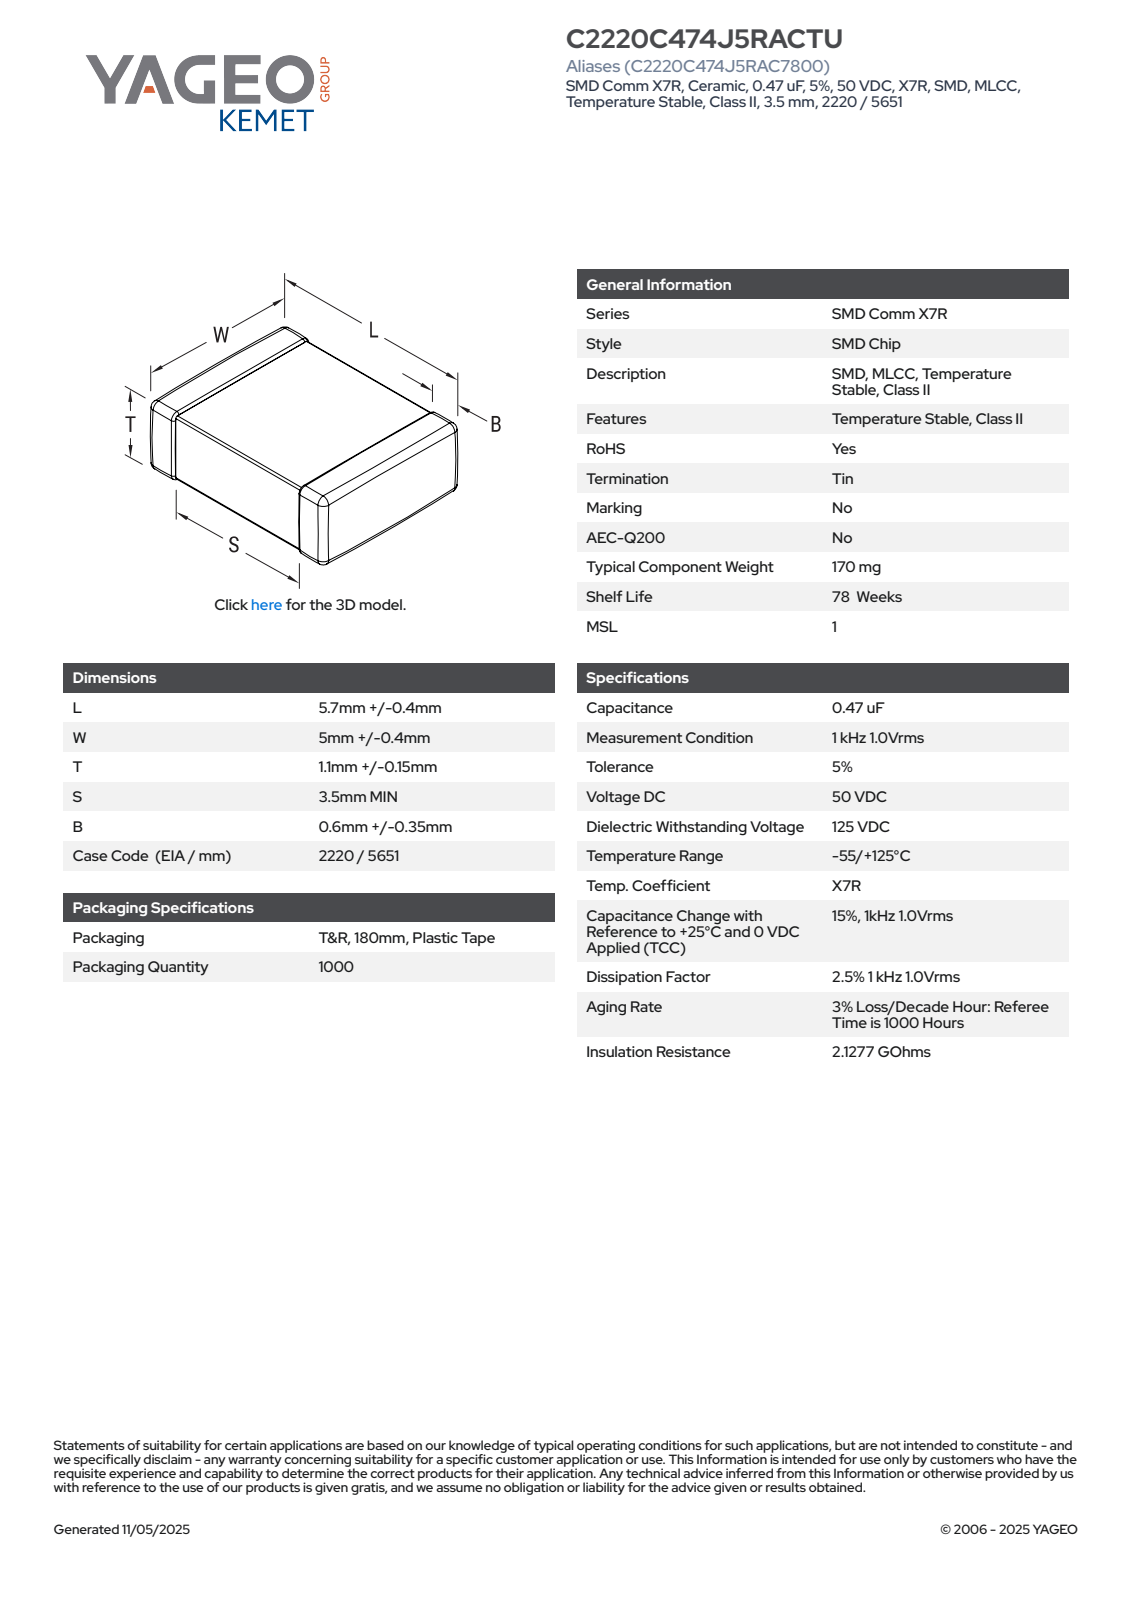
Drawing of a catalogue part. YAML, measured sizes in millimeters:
part_name: "CCS_CCSTDNOS_2220_L6.1W5.4T1.25B0.95"
step_written_by: "SolidWorks 2014 (AUTOMOTIVE_DESIGN)"
units: millimeters
bodies: {solids: 4, faces: 125, planar: 71, cylindrical: 38, other: 16}
overall_size: [6.1, 5.4, 1.25]
volume: 35
surface_area: 91
partial_cylinders:
  - {radius: 0.11, count: 24}
face_to_face_distances: [1.03, 1.14, 1.25, 6.1, 5.18, 5.29, 5.4, 2.66, 2.74, 2.55]
